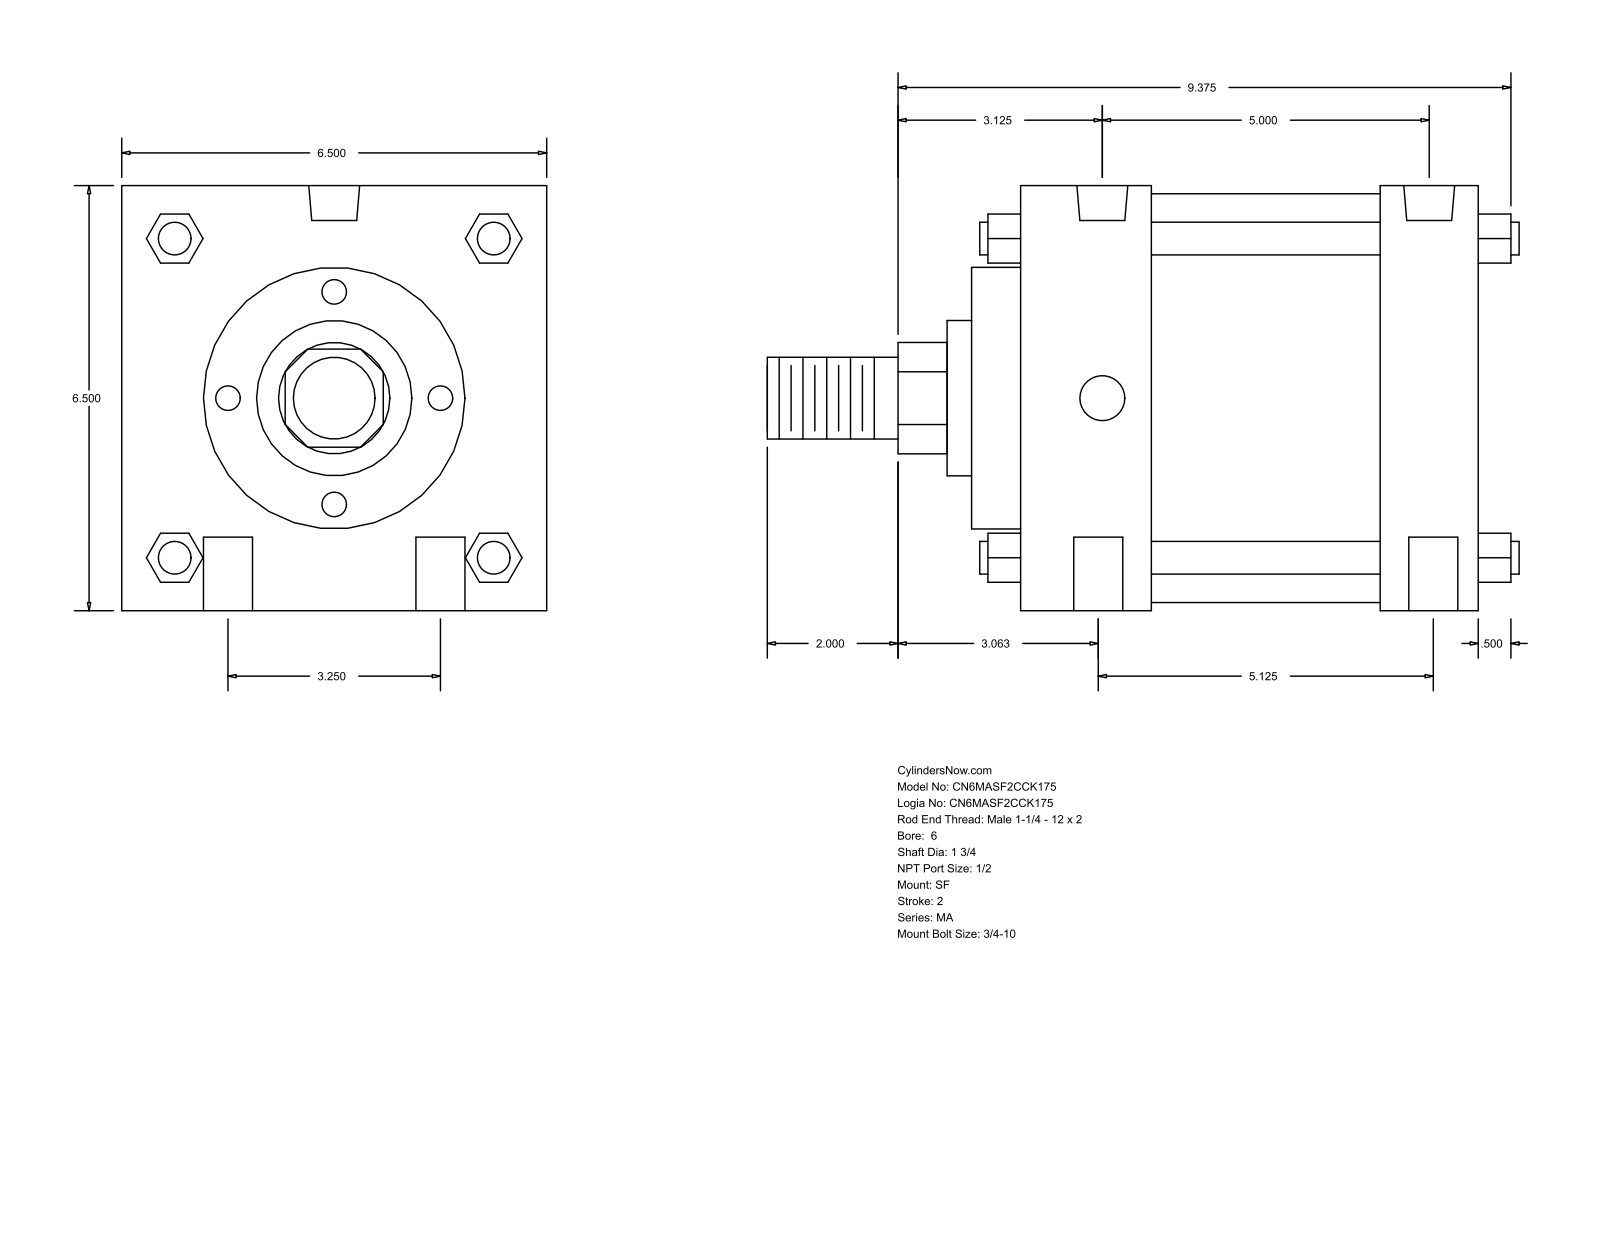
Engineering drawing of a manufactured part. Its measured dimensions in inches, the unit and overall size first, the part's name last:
Units: inches
Overall size (bounding box): 11.5 × 6.5 × 6.5
Round holes (diameter × count): ⌀0.75 ×4, ⌀0.687 ×2, ⌀0.778 ×2
Round bosses / shafts (diameter × count): ⌀0.5 ×4, ⌀6.25 ×1, ⌀4 ×1, ⌀2.375 ×1, ⌀1.75 ×1, ⌀1.25 ×1
Partial cylindrical surfaces — rounded edges, fillets, slot ends (radius × count): R0.852 ×1
Main face-to-face distances: 6.5, 7, 0.75, 2, 5.5, 3.5, 1.5, 5, 2.75, 6.25
Hole centre spacings: 1.626, 3.25, 5, 5.125, 5.317, 5.317, 6.068
Bodies: 0 solids, 126 faces (95 planar, 31 cylindrical, 0 other)
Part name (STEP PRODUCT): MA_SF__0600_1.75
STEP written by: GSSL Pune (CONFIG_CONTROL_DESIGN)
